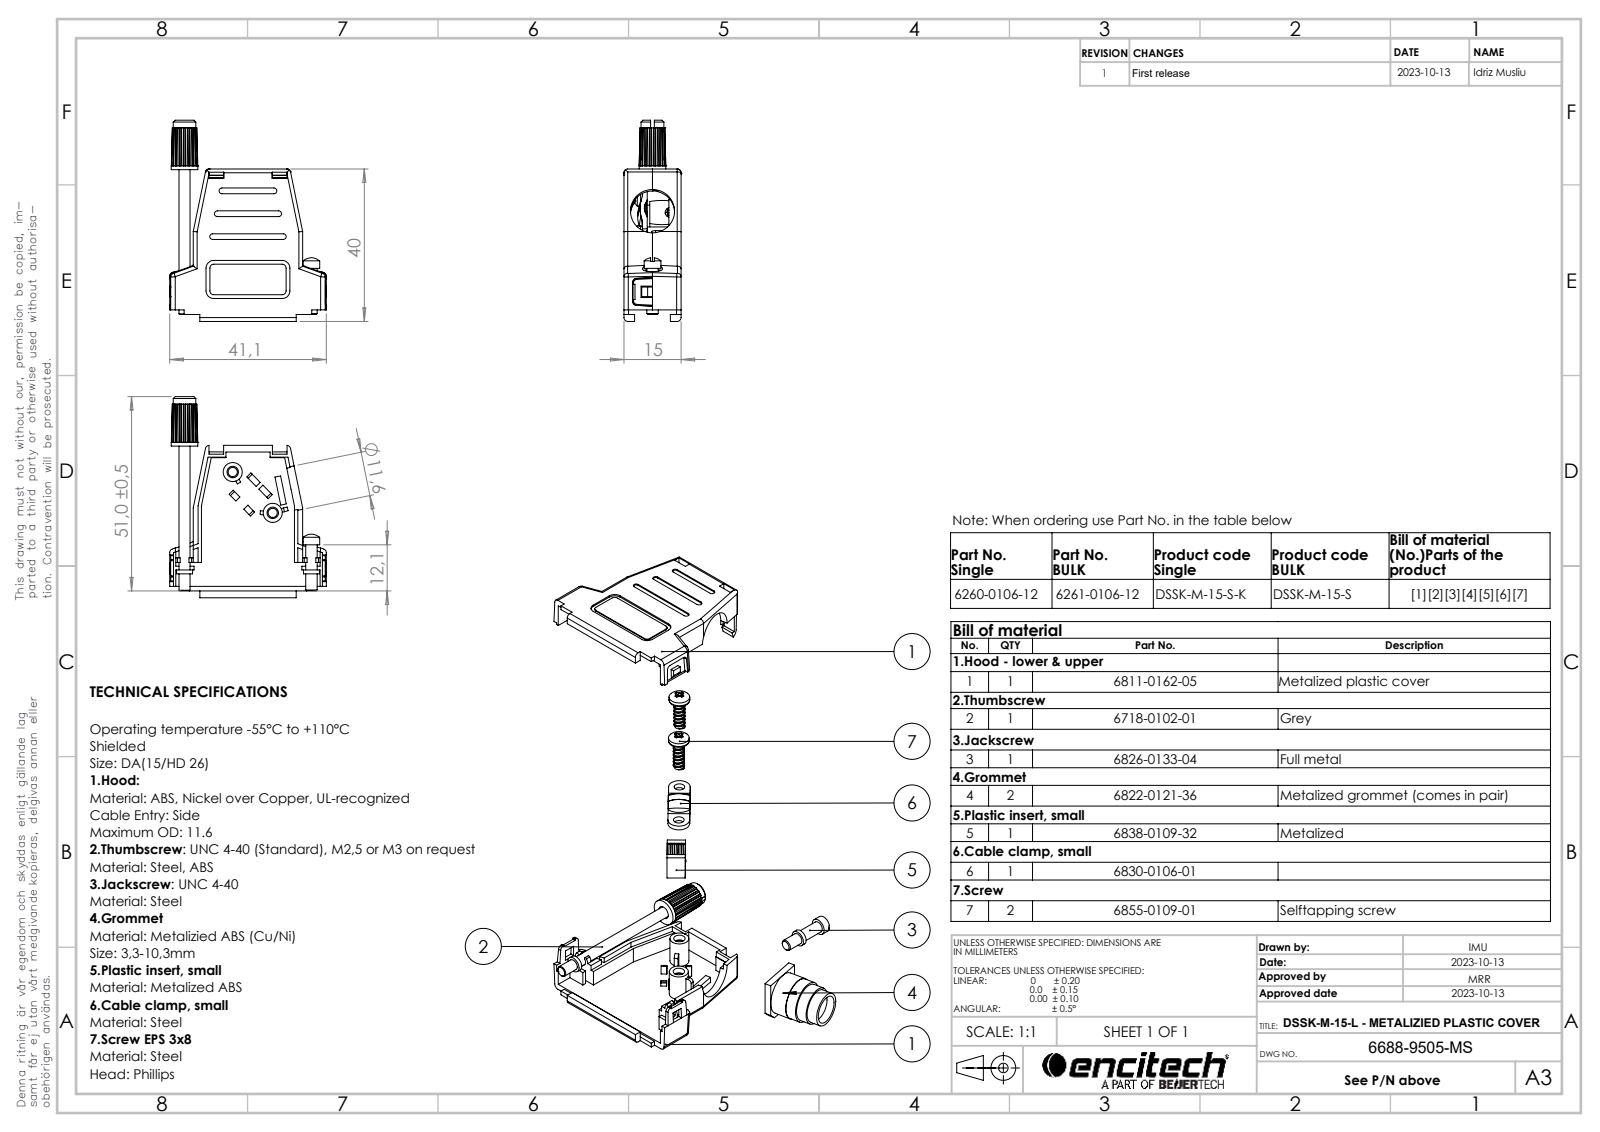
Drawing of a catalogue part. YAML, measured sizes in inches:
part_name: "6855-0109-01; 6688-9505-MS; 6826-0133-04; 6811-0162-05 Part 2 (+5 more)"
step_written_by: "SolidWorks 2021 (AUTOMOTIVE_DESIGN)"
units: inches
bodies: {solids: 11, faces: 1029, planar: 666, cylindrical: 278, other: 85}
overall_size: [2.079, 1.819, 0.591]
volume: 0.481
surface_area: 19.13
round_holes:
  - {diameter: 0.094, count: 2}
  - {diameter: 0.11, count: 2}
  - {diameter: 0.118, count: 2}
  - {diameter: 0.03, count: 1}
  - {diameter: 0.035, count: 1}
  - {diameter: 0.049, count: 1}
  - {diameter: 0.098, count: 1}
  - {diameter: 0.138, count: 1}
  - {diameter: 0.295, count: 1}
  - {diameter: 0.335, count: 1}
  - {diameter: 0.374, count: 1}
  - {diameter: 0.413, count: 1}
round_bosses_or_shafts:
  - {diameter: 0.215, count: 2}
  - {diameter: 0.197, count: 2}
  - {diameter: 0.165, count: 2}
  - {diameter: 0.097, count: 2}
  - {diameter: 0.445, count: 1}
  - {diameter: 0.437, count: 1}
  - {diameter: 0.398, count: 1}
  - {diameter: 0.358, count: 1}
partial_cylinders:
  - {radius: 0.039, count: 31}
  - {radius: 0.01, count: 24}
  - {radius: 0.02, count: 20}
  - {radius: 0.005, count: 16}
  - {radius: 0.03, count: 6}
  - {radius: 0.079, count: 6}
  - {radius: 0.016, count: 4}
  - {radius: 0.047, count: 4}
face_to_face_distances: [0.067, 0.524, 0.457, 0.591, 0.295, 0.228, 0.287, 0.059, 0.047, 0.583]
hole_center_spacings: [0.535, 0.284, 0.307, 0.309, 0.323, 0.337, 0.365, 0.366]
